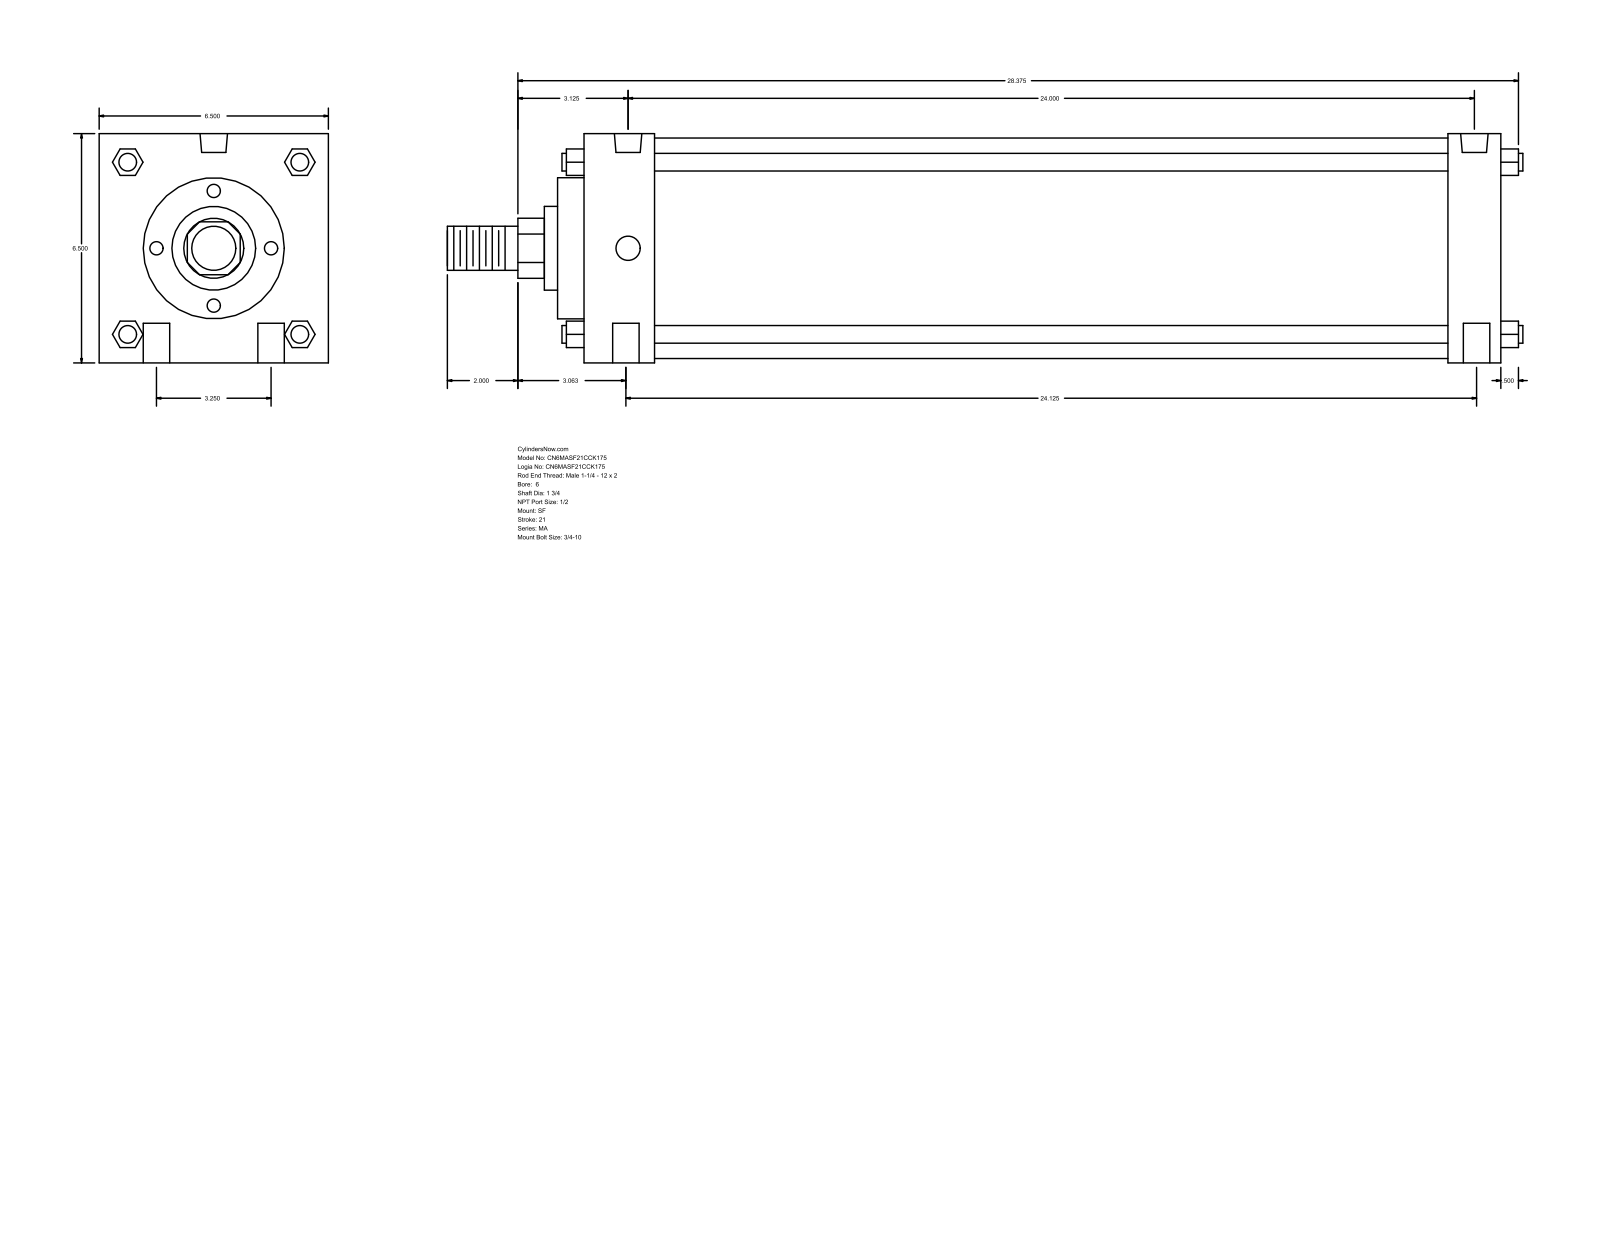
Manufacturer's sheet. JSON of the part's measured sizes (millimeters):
{"part_name": "MA_SF__0600_1.75", "step_written_by": "GSSL Pune (CONFIG_CONTROL_DESIGN)", "units": "millimeters", "bodies": {"solids": 0, "faces": 126, "planar": 95, "cylindrical": 31, "other": 0}, "overall_size": [774.7, 165.1, 165.1], "round_holes": [[19.05, 4], [17.46, 2], [19.77, 2]], "round_bosses_or_shafts": [[12.7, 4], [158.75, 1], [101.6, 1], [60.33, 1], [44.45, 1], [31.75, 1]], "partial_cylinders_radius": [[21.63, 1]], "face_to_face_distances": [165.1, 660.4, 19.05, 50.8, 38.1, 622.3, 571.5, 609.6, 69.85, 641.35], "hole_center_spacings": [41.3, 82.54, 609.6, 612.57, 612.58, 612.77, 618.3]}
